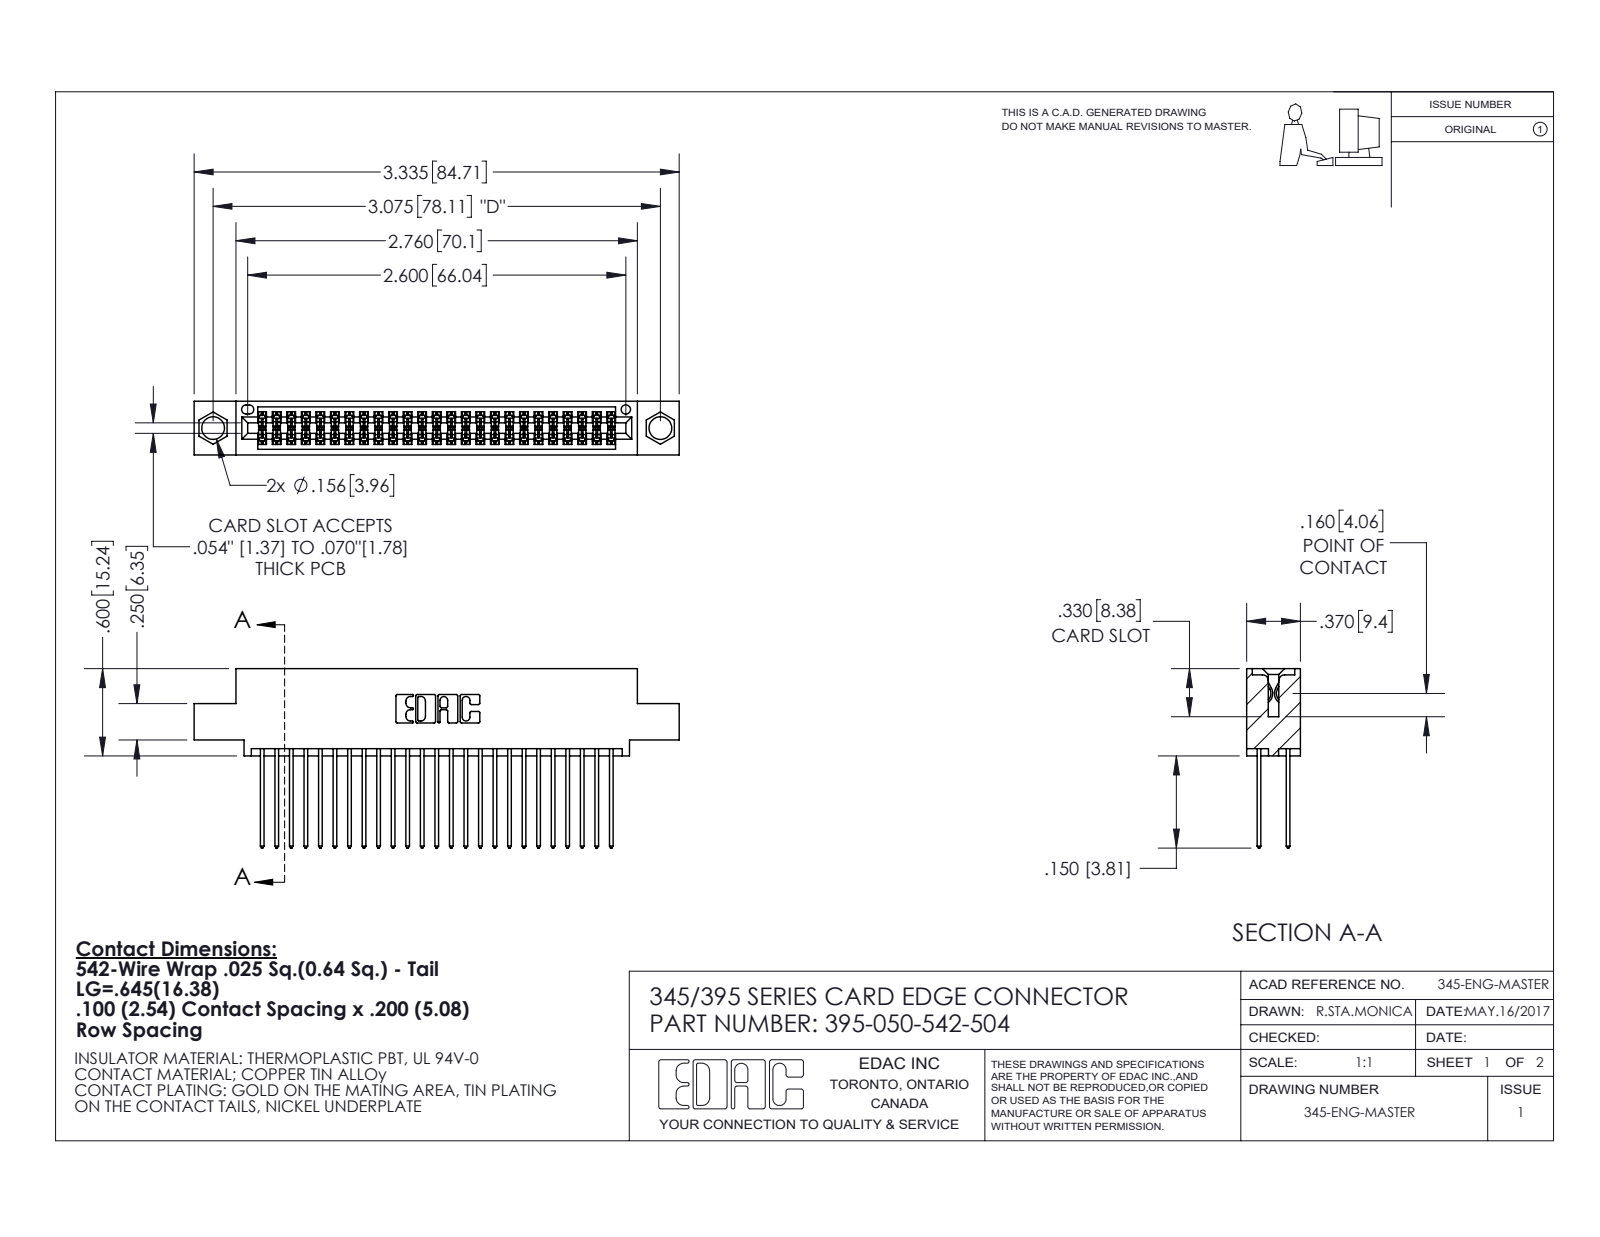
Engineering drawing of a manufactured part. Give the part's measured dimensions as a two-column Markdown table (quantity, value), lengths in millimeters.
| quantity | value |
| --- | --- |
| part name | 345-292-001_345-293-142; 395-050-542-504; 345 Part_0.110 Offset - 0.156 Dia-TI |
| STEP written by | SolidWorks 2020 (CONFIG_CONTROL_DESIGN) |
| units | millimeters |
| bodies | 51 solids, 2644 faces (1748 planar, 896 cylindrical, 0 other) |
| overall size | 84.7 × 31.3 × 9.4 |
| volume | 8 130 mm³ |
| surface area | 12 720 mm² |
| round holes (diameter × count) | 4 × 2, 1.6 × 1 |
| partial cylindrical surfaces (radius × count) | 0.2 × 75, 0.3 × 50, 0.3 × 22, 0.2 × 6, 0.8 × 6, 0.7 × 3, 0.4 × 2, 0.5 × 2 |
| main face-to-face distances | 7.6, 1.8, 5.1, 2.5, 6.9, 0.6, 9.4, 5.7, 4.4, 3.8 |
| hole center spacings | 6.9, 72.1, 78.1 |
